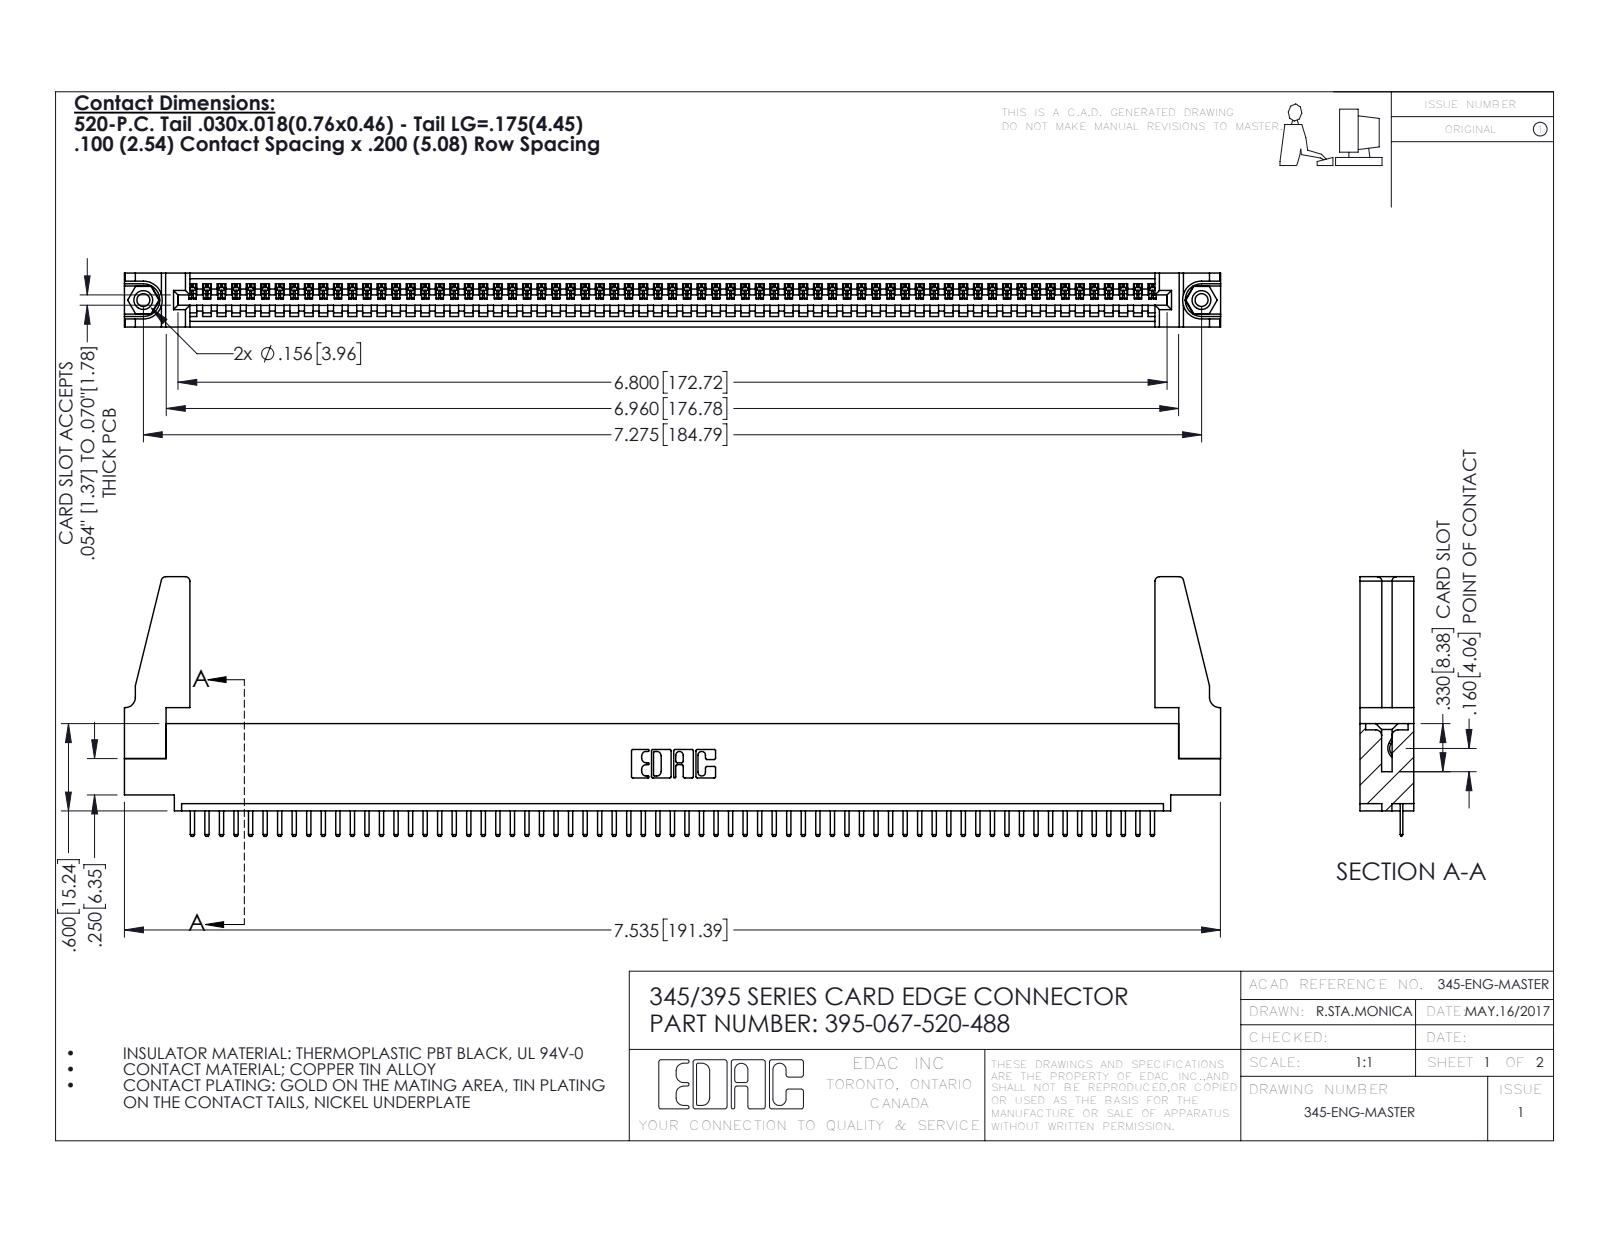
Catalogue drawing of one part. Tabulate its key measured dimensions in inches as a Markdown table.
| quantity | value |
| --- | --- |
| part name | 345-250-001_345-250-001-102; 345 Part_0.110 Offset - 0.156 Dia-TH; 345-292-001_345-293-120; 345-220-078_345-220-088 (+1 more) |
| STEP written by | SolidWorks 2016 (CONFIG_CONTROL_DESIGN) |
| units | inches |
| bodies | 72 solids, 4408 faces (2970 planar, 1422 cylindrical, 16 other) |
| overall size | 7.536 × 1.785 × 0.37 |
| volume | 1.304 in³ |
| surface area | 41.85 in² |
| round holes (diameter × count) | 0.089 × 2, 0.125 × 2, 0.156 × 2, 0.064 × 1 |
| round bosses / shafts (diameter × count) | 0.155 × 2 |
| partial cylindrical surfaces (radius × count) | 0.01 × 136, 0.006 × 134, 0.01 × 22, 0.03 × 8, 0.007 × 6, 0.031 × 6, 0.026 × 3, 0.031 × 2 |
| main face-to-face distances | 0.072, 0.298, 0.37, 0.098, 0.272, 0.025, 0.2, 0.225, 0.072, 0.149 |
| hole center spacings | 0.27, 7.039, 7.275 |
